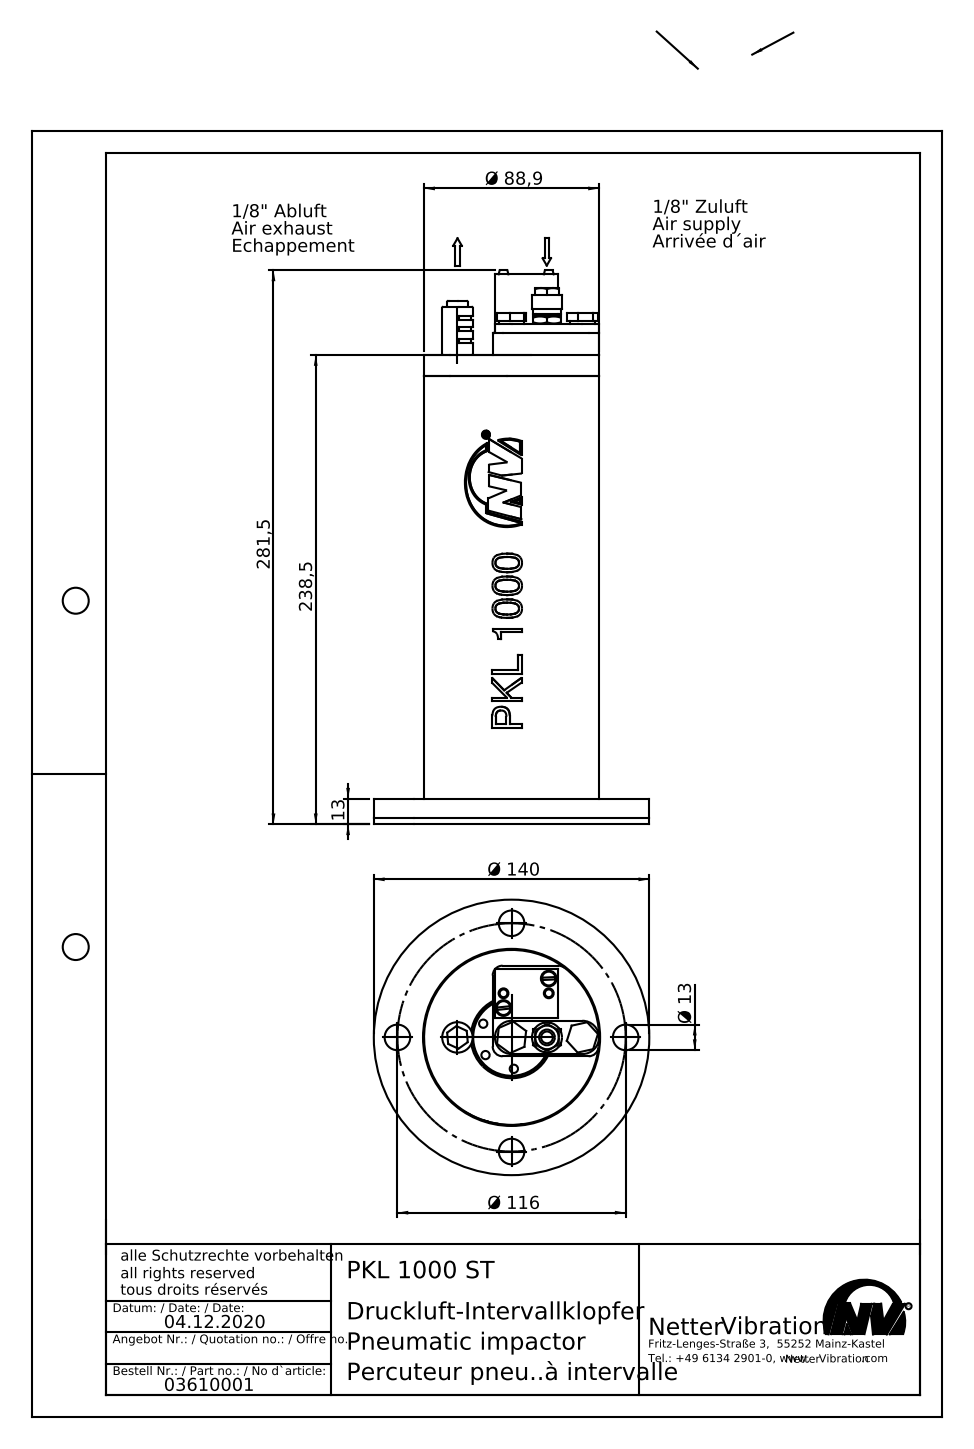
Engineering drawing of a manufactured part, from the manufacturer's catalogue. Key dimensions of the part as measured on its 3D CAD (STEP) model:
Part name (STEP PRODUCT): PKL 1000 ST
STEP written by: SolidWorks 2015 (CONFIG_CONTROL_DESIGN)
Units: millimetres
Bodies: 21 solids, 706 faces (191 planar, 232 cylindrical, 283 other)
Overall size (bounding box): 281.7 × 140 × 140
Volume: 1 838 000 mm³ · Surface area: 211 161 mm²
Round holes (diameter × count): ⌀4.2 ×6, ⌀13 ×4, ⌀3.5 ×3, ⌀4 ×3, ⌀8 ×3, ⌀4.5 ×2, ⌀5 ×2, ⌀8.57 ×2, ⌀10 ×2, ⌀1.5 ×1, ⌀6 ×1, ⌀6.81 ×1
Round bosses / shafts (diameter × count): ⌀9.73 ×3, ⌀13 ×2, ⌀9.6 ×2, ⌀8.94 ×2, ⌀4 ×2, ⌀140 ×1, ⌀88.9 ×1, ⌀86 ×1
Partial cylindrical surfaces — rounded edges, fillets, slot ends (radius × count): R0.5 ×18, R5 ×4, R1 ×2, R8.45 ×2, R7 ×1, R44.55 ×1
Main face-to-face distances: 215.5, 3, 10, 10.5, 9.5, 238.5, 235.5, 20, 13, 225.5
Hole centre spacings: 16, 27.71, 58, 82.02, 32, 5.75, 7.5, 11.5
